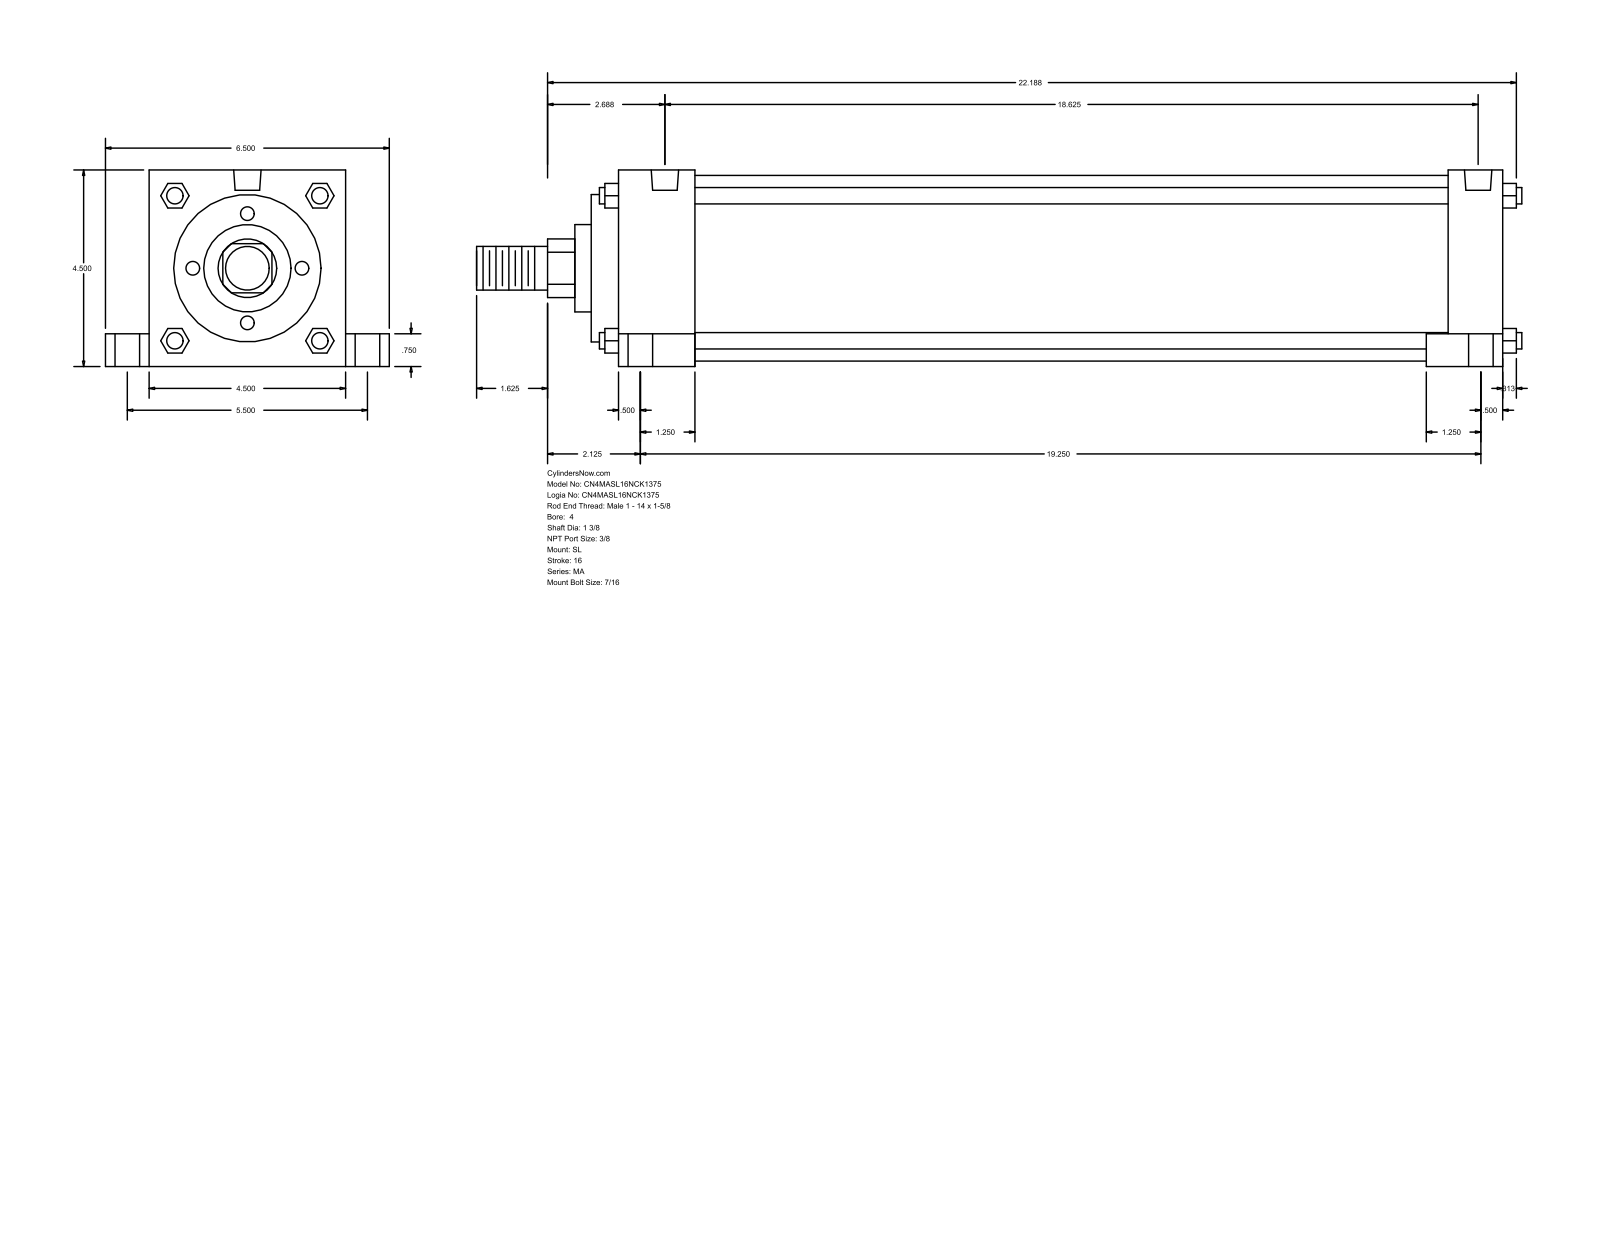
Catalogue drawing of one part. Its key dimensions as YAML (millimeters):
part_name: "MA_SL__0400_1.375"
step_written_by: "GSSL Pune (CONFIG_CONTROL_DESIGN)"
units: millimeters
bodies: {solids: 0, faces: 150, planar: 113, cylindrical: 37, other: 0}
overall_size: [608.01, 165.1, 114.3]
round_holes:
  - {diameter: 11.11, count: 4}
  - {diameter: 14.29, count: 4}
  - {diameter: 20.64, count: 4}
  - {diameter: 15.93, count: 2}
round_bosses_or_shafts:
  - {diameter: 9.53, count: 4}
  - {diameter: 107.95, count: 1}
  - {diameter: 85.72, count: 1}
  - {diameter: 50.8, count: 1}
  - {diameter: 34.92, count: 1}
  - {diameter: 25.4, count: 1}
partial_cylinders:
  - {radius: 17.06, count: 1}
face_to_face_distances: [114.3, 514.35, 530.22, 15.87, 60.32, 44.45, 469.9, 498.48, 482.61, 438.16]
hole_center_spacings: [69.87, 70.14, 71.29, 72.4, 139.7, 463.55, 475.05, 479.77]
